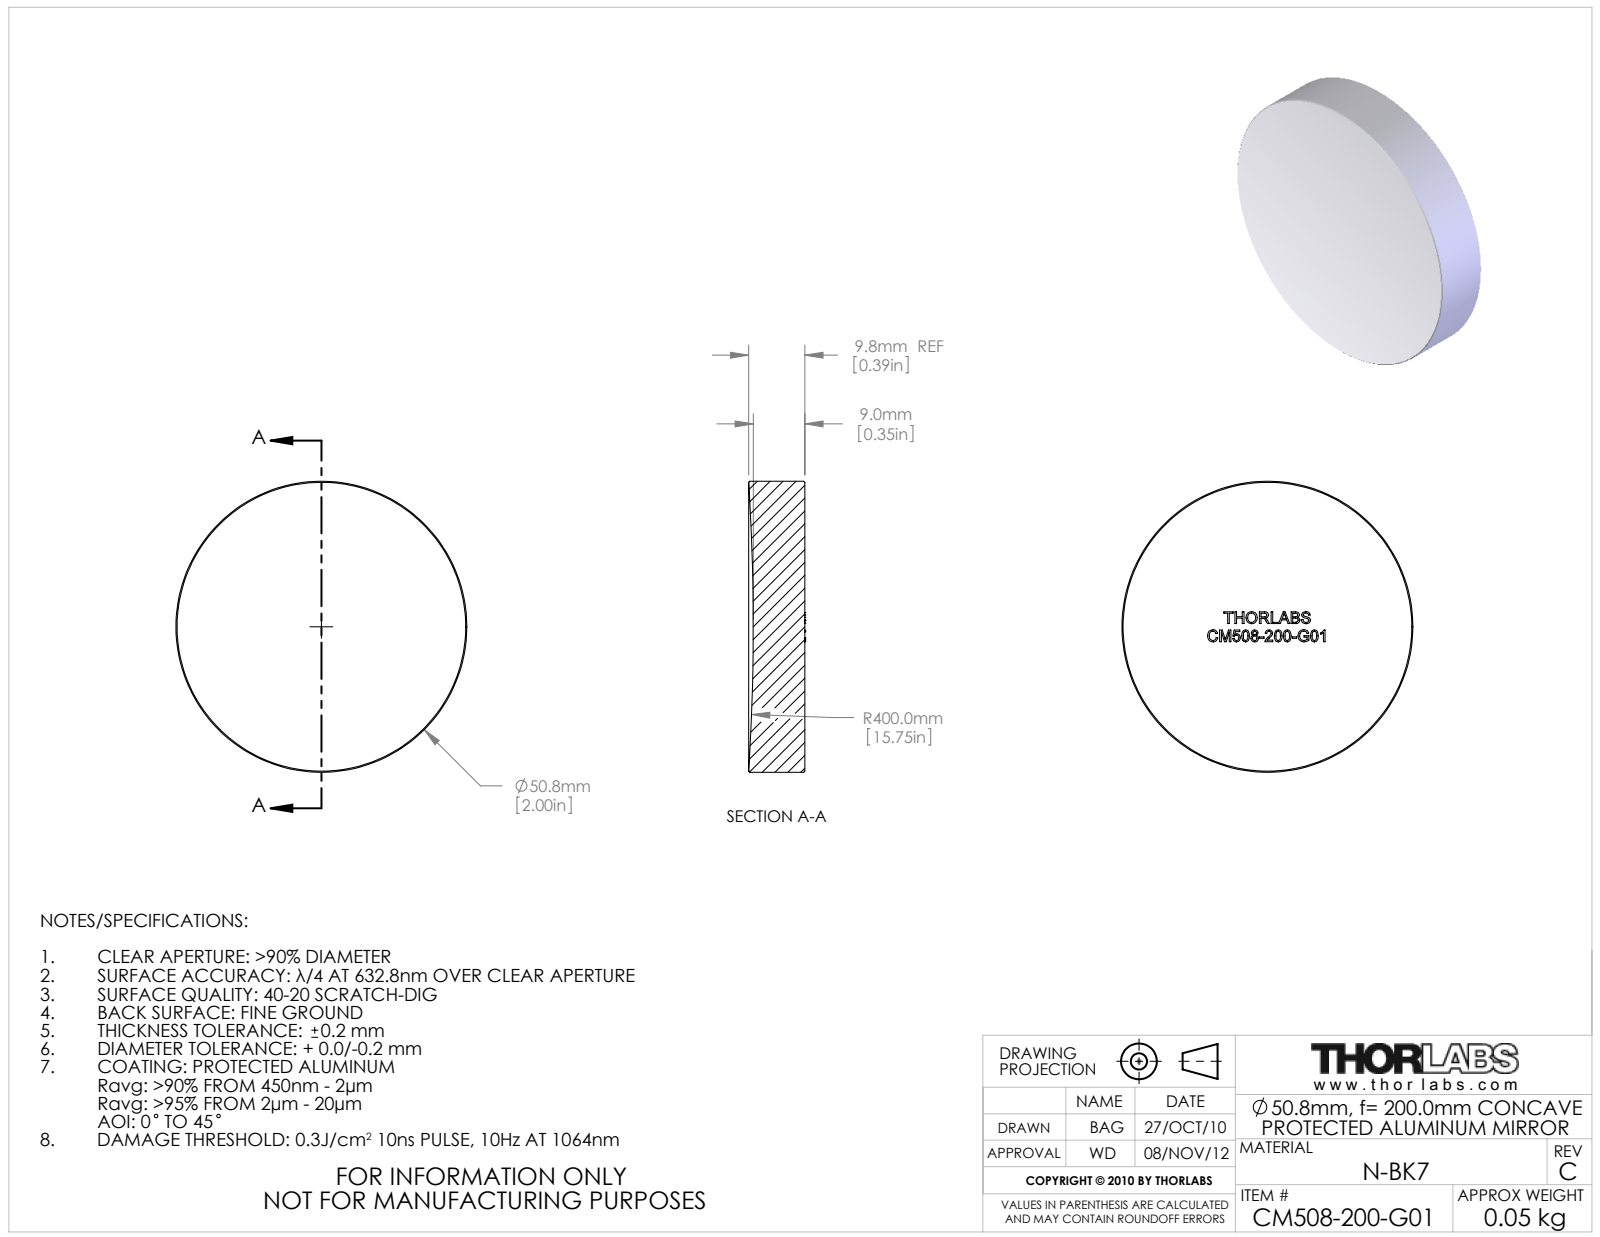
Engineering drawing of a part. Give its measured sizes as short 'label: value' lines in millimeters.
name: 12016-E0W
written by: SolidWorks 2009 (AUTOMOTIVE_DESIGN)
unit: mm
bodies: 1 solid, 282 faces (137 planar, 2 cylindrical, 143 other)
size: 50.8 × 50.8 × 9.8
volume: 19 060 mm³; area: 5 582 mm²
bosses: 1× ⌀50.8
face distances: 5.5, 1, 5.2, 2.1, 1.4, 2.6, 7.3, 3, 2.1, 7.6
